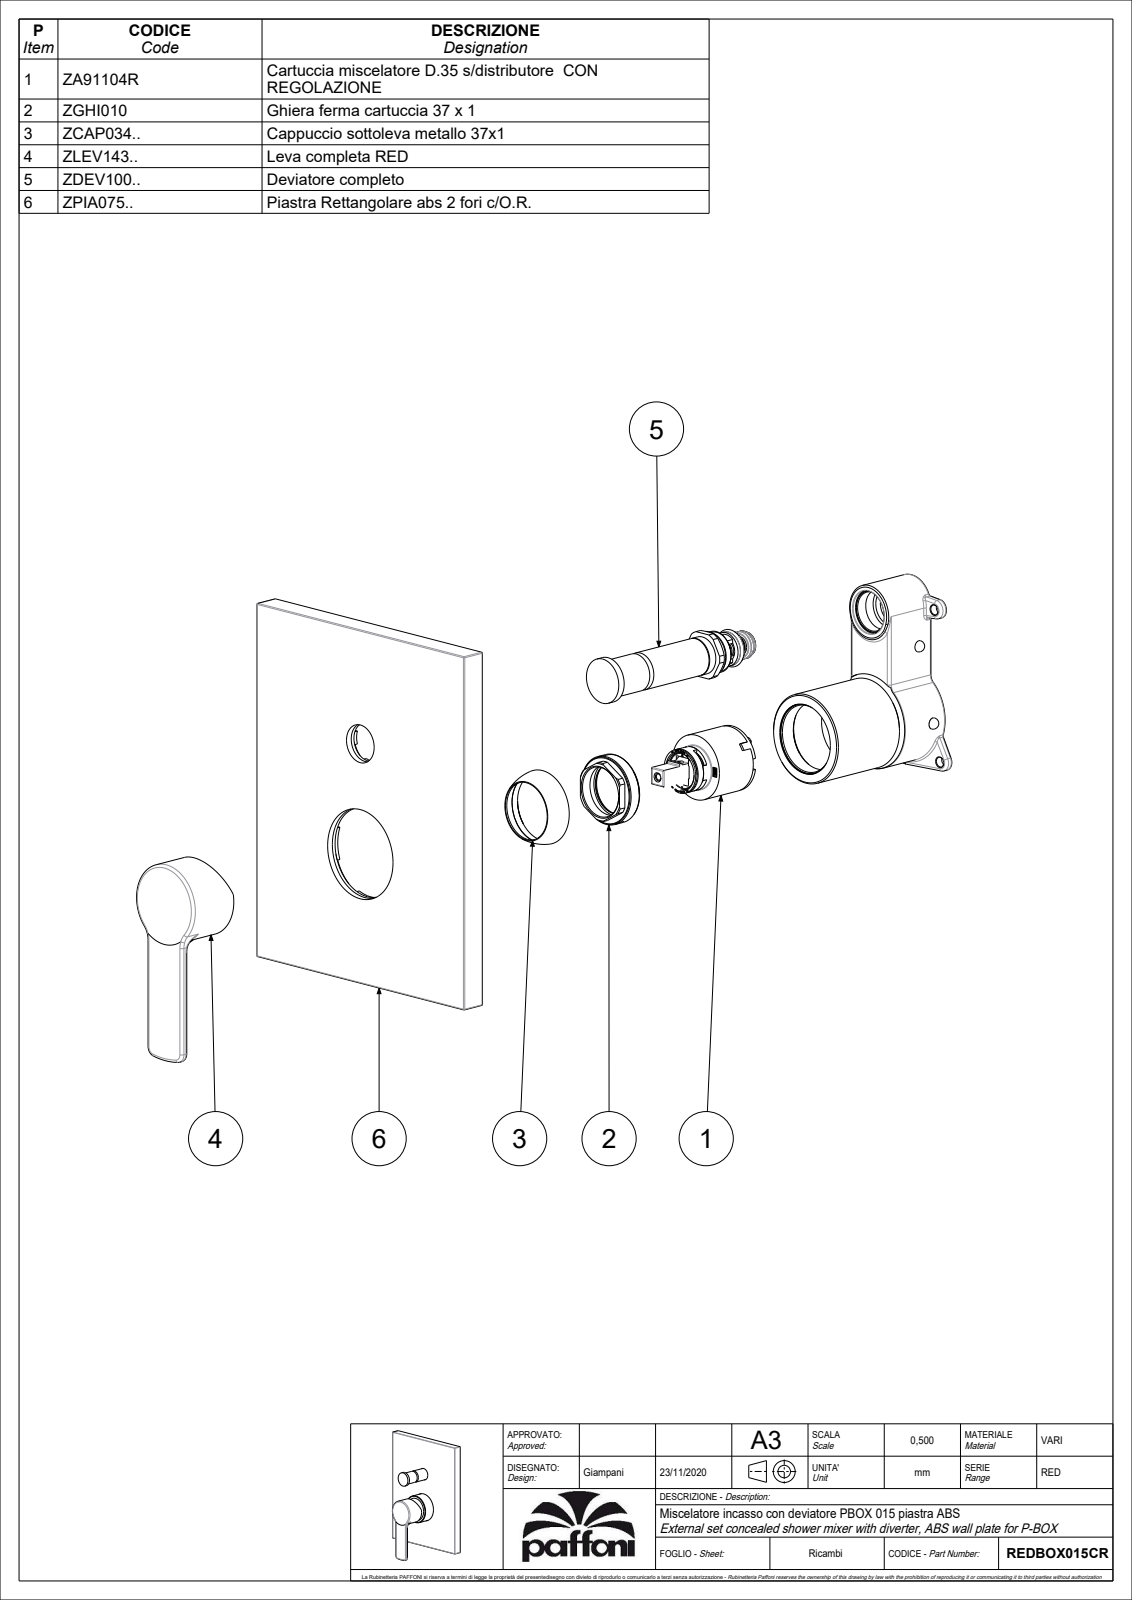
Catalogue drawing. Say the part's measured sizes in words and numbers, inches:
The part is named "REDBOX015CR". Its 3-D file was written by "CREO PARAMETRIC BY PTC INC, 2020044 (CONFIG_CONTROL_DESIGN)". It is 5 solids with 1216 faces: 669 planar, 327 cylindrical and 220 other. Overall it measures 8.14 by 6.063 by 2.769 inches. Its volume is 19.97 cubic inches and its surface area 197.6 square inches. Round holes: 3 of diameter 0.197, 3 of diameter 0.276, 2 of diameter 0.079, 2 of diameter 0.13, 2 of diameter 0.157, 1 of diameter 0.118, 1 of diameter 0.177, 1 of diameter 0.28, 1 of diameter 0.63, 1 of diameter 0.717, 1 of diameter 0.768, 1 of diameter 0.783. Round bosses or shafts: 2 of diameter 0.189, 1 of diameter 2.244, 1 of diameter 1.894, 1 of diameter 1.693, 1 of diameter 1.535, 1 of diameter 1.378, 1 of diameter 1.37, 1 of diameter 1.268. Partial cylindrical surfaces (rounded edges, fillets, slot ends): 74 of radius 0.02, 11 of radius 0.006, 4 of radius 0.012, 4 of radius 0.059, 2 of radius 0.039, 2 of radius 0.197, 2 of radius 0.394, 1 of radius 0.098. The main face-to-face distances are 0.531, 0.394, 0.138, 0.925, 5.138, 6.063, 0.177, 6.634, 2.366, 7.559. The hole center spacings are 0.339, 0.53, 0.596, 0.863, 2, 2.574, 0.492, 0.551.
